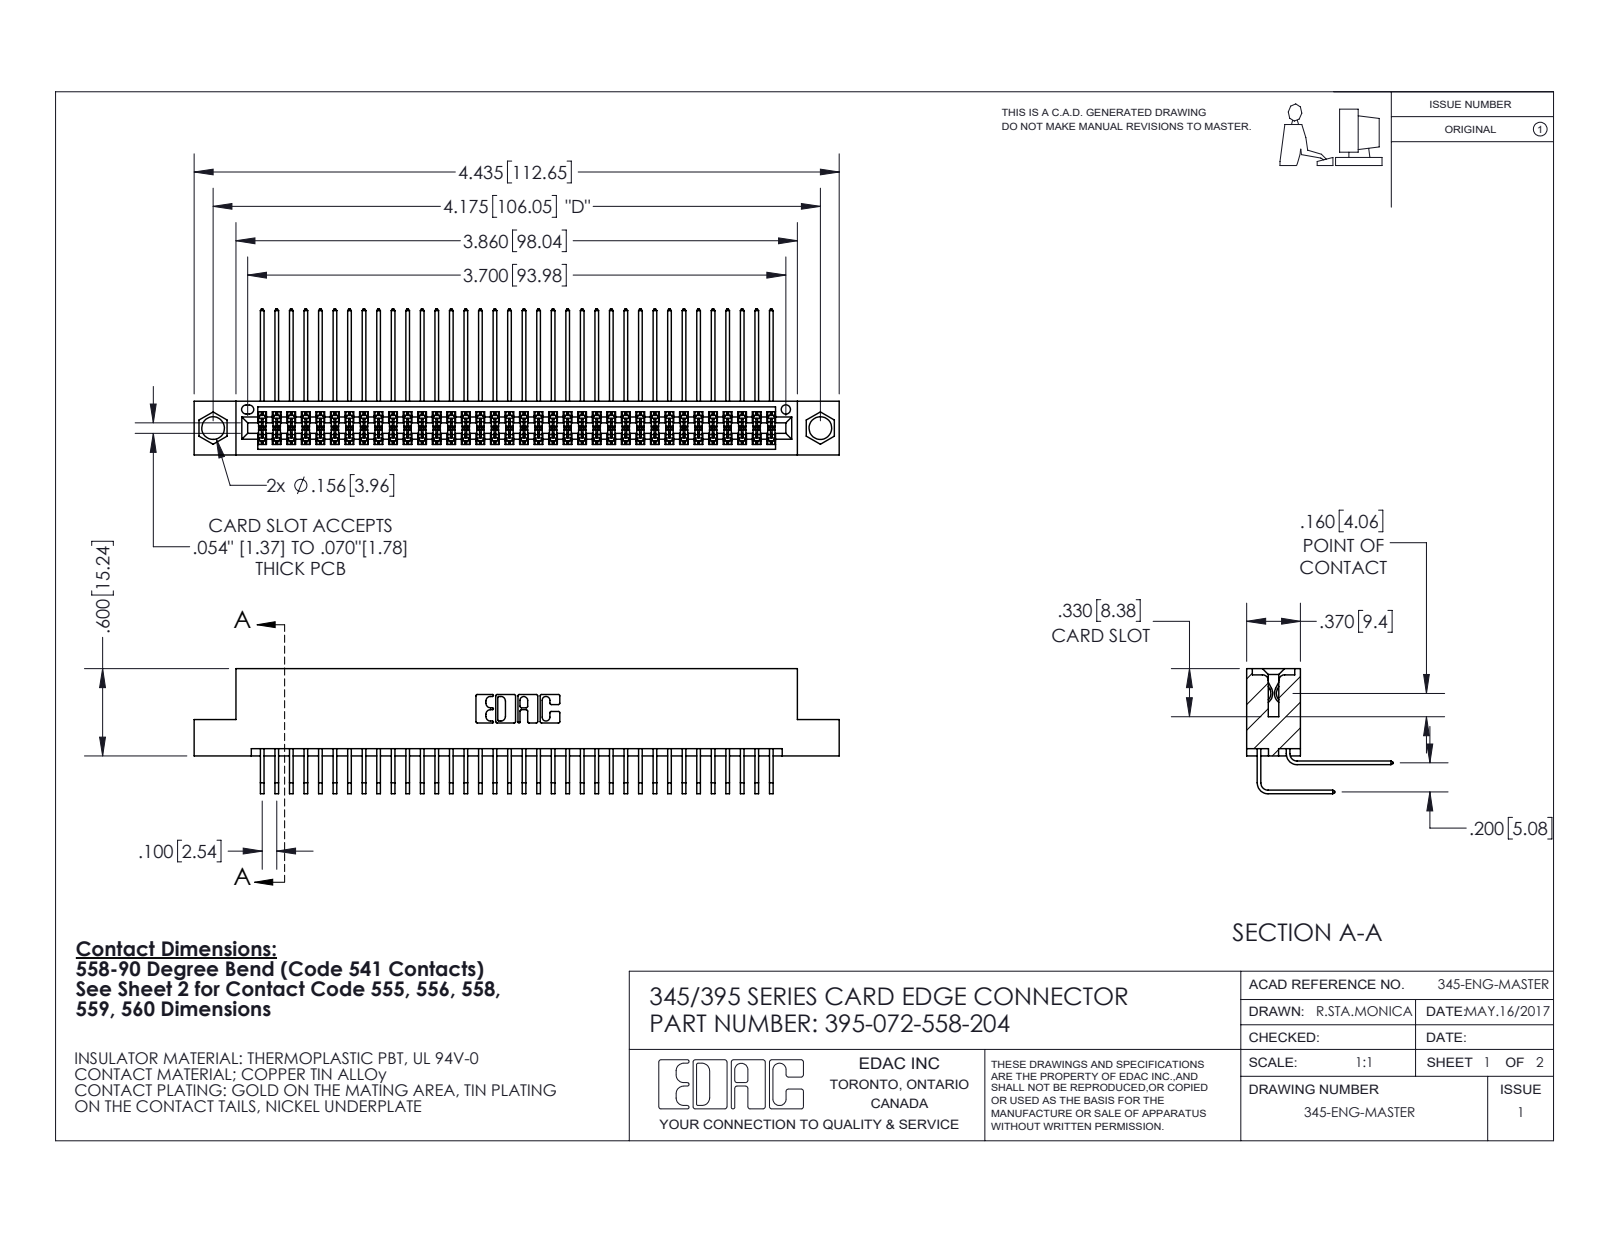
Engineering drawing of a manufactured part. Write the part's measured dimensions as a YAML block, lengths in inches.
part_name: "345-292-001_558 559 Tail - 1; 345-292-001_558 Tail - 2; 395-072-558-204; 345 Part_Flush Mounting Lugs - 0.156 Dia-TI"
step_written_by: "SolidWorks 2020 (CONFIG_CONTROL_DESIGN)"
units: inches
bodies: {solids: 73, faces: 3884, planar: 2614, cylindrical: 1270, other: 0}
overall_size: [4.435, 1.005, 0.859]
volume: 0.683
surface_area: 28.27
round_holes:
  - {diameter: 0.156, count: 2}
  - {diameter: 0.064, count: 1}
partial_cylinders:
  - {radius: 0.006, count: 108}
  - {radius: 0.01, count: 22}
  - {radius: 0.007, count: 6}
  - {radius: 0.031, count: 6}
  - {radius: 0.026, count: 3}
  - {radius: 0.014, count: 2}
  - {radius: 0.019, count: 2}
  - {radius: 0.022, count: 2}
face_to_face_distances: [0.072, 0.298, 0.2, 0.37, 0.098, 0.272, 0.025, 0.225, 0.025, 0.175]
hole_center_spacings: [0.27, 3.939, 4.175]
